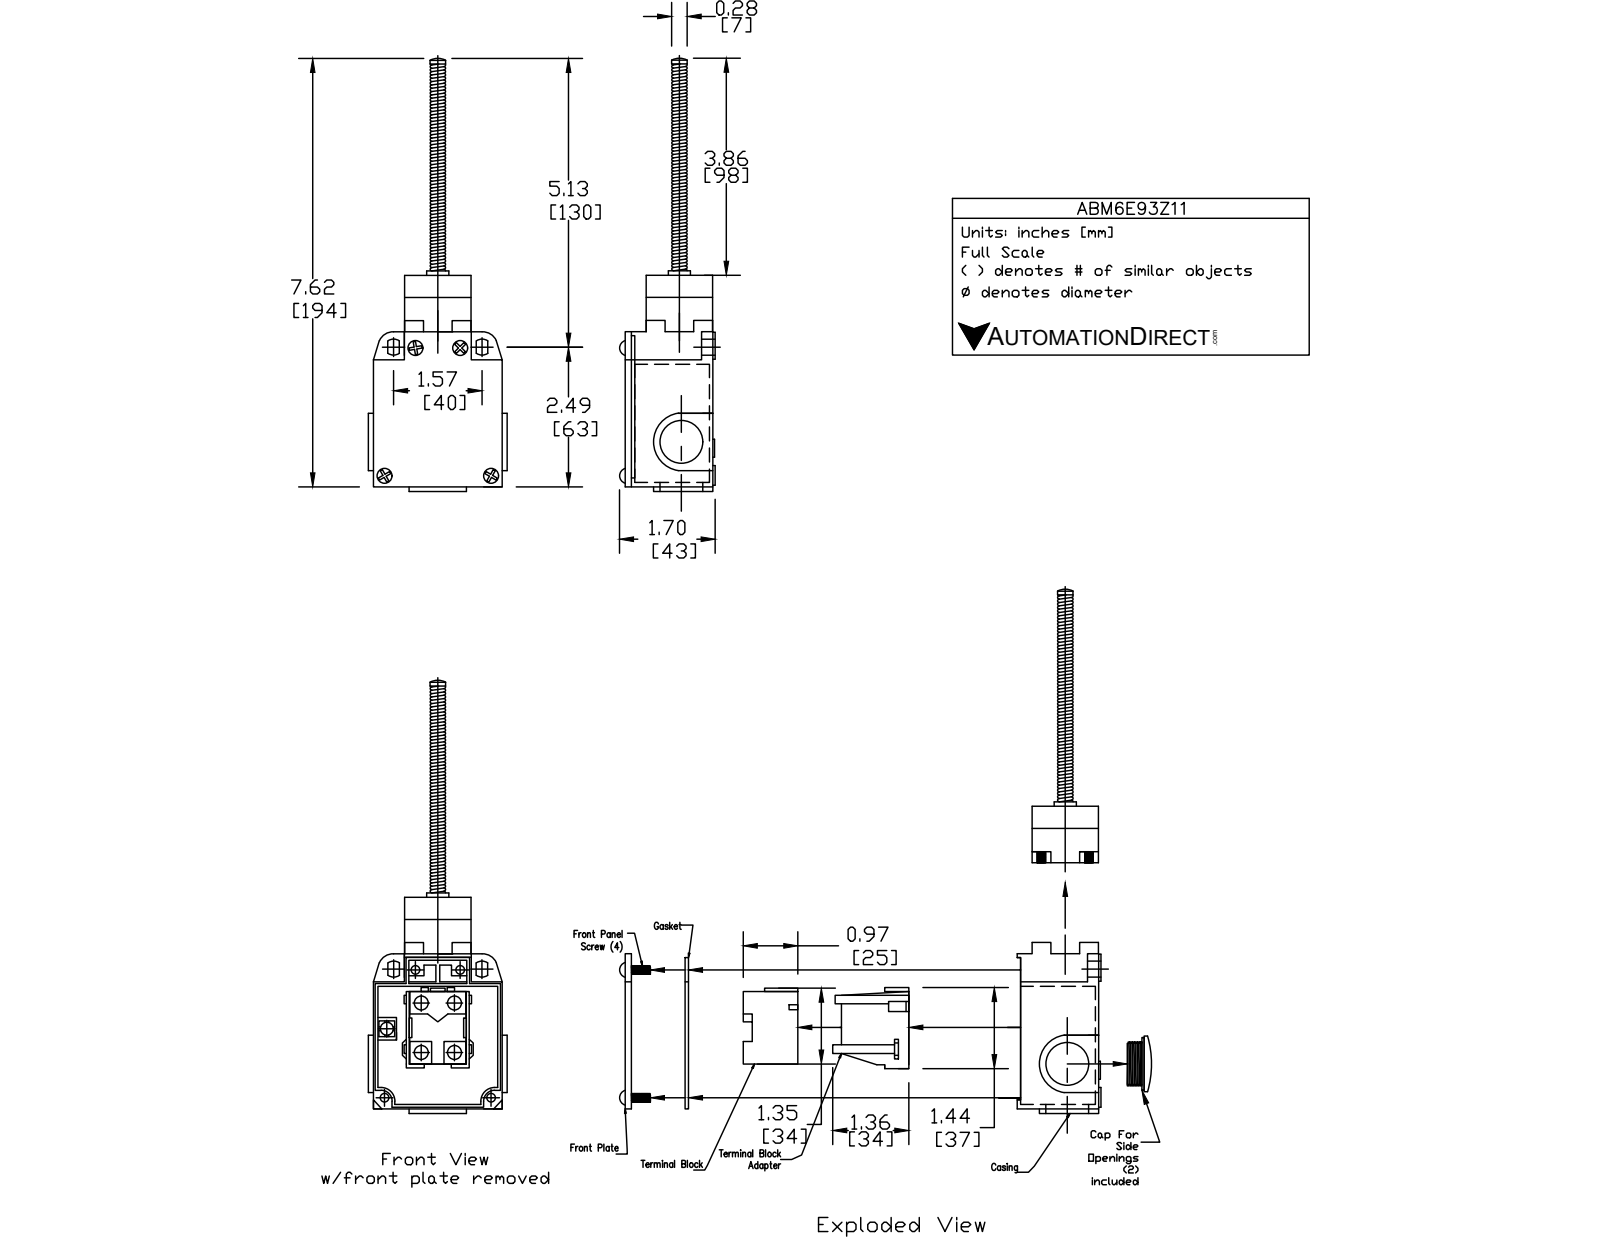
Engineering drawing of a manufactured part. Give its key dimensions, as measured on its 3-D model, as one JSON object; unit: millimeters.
{"part_name": "ABM6E93Z11", "step_written_by": "SolidWorks 2017 (AUTOMOTIVE_DESIGN)", "units": "millimeters", "bodies": {"solids": 3, "faces": 217, "planar": 87, "cylindrical": 88, "other": 42}, "overall_size": [193.8, 62, 43.3], "volume_mm3": 168800, "surface_area_mm2": 27010, "round_holes": [[17, 2], [19, 2], [20.5, 1]], "round_bosses_or_shafts": [[7, 9], [12, 2], [9, 2], [19, 1], [11.7, 1], [6.8, 1]], "partial_cylinders_radius": [[1.5, 12], [0.5, 4], [0.6, 4], [3.7, 2], [6.5, 2], [13, 2], [11.5, 1], [12, 1]], "face_to_face_distances": [39.5, 44, 14, 58, 30, 2, 70, 6, 13, 16], "hole_center_spacings": [1]}
